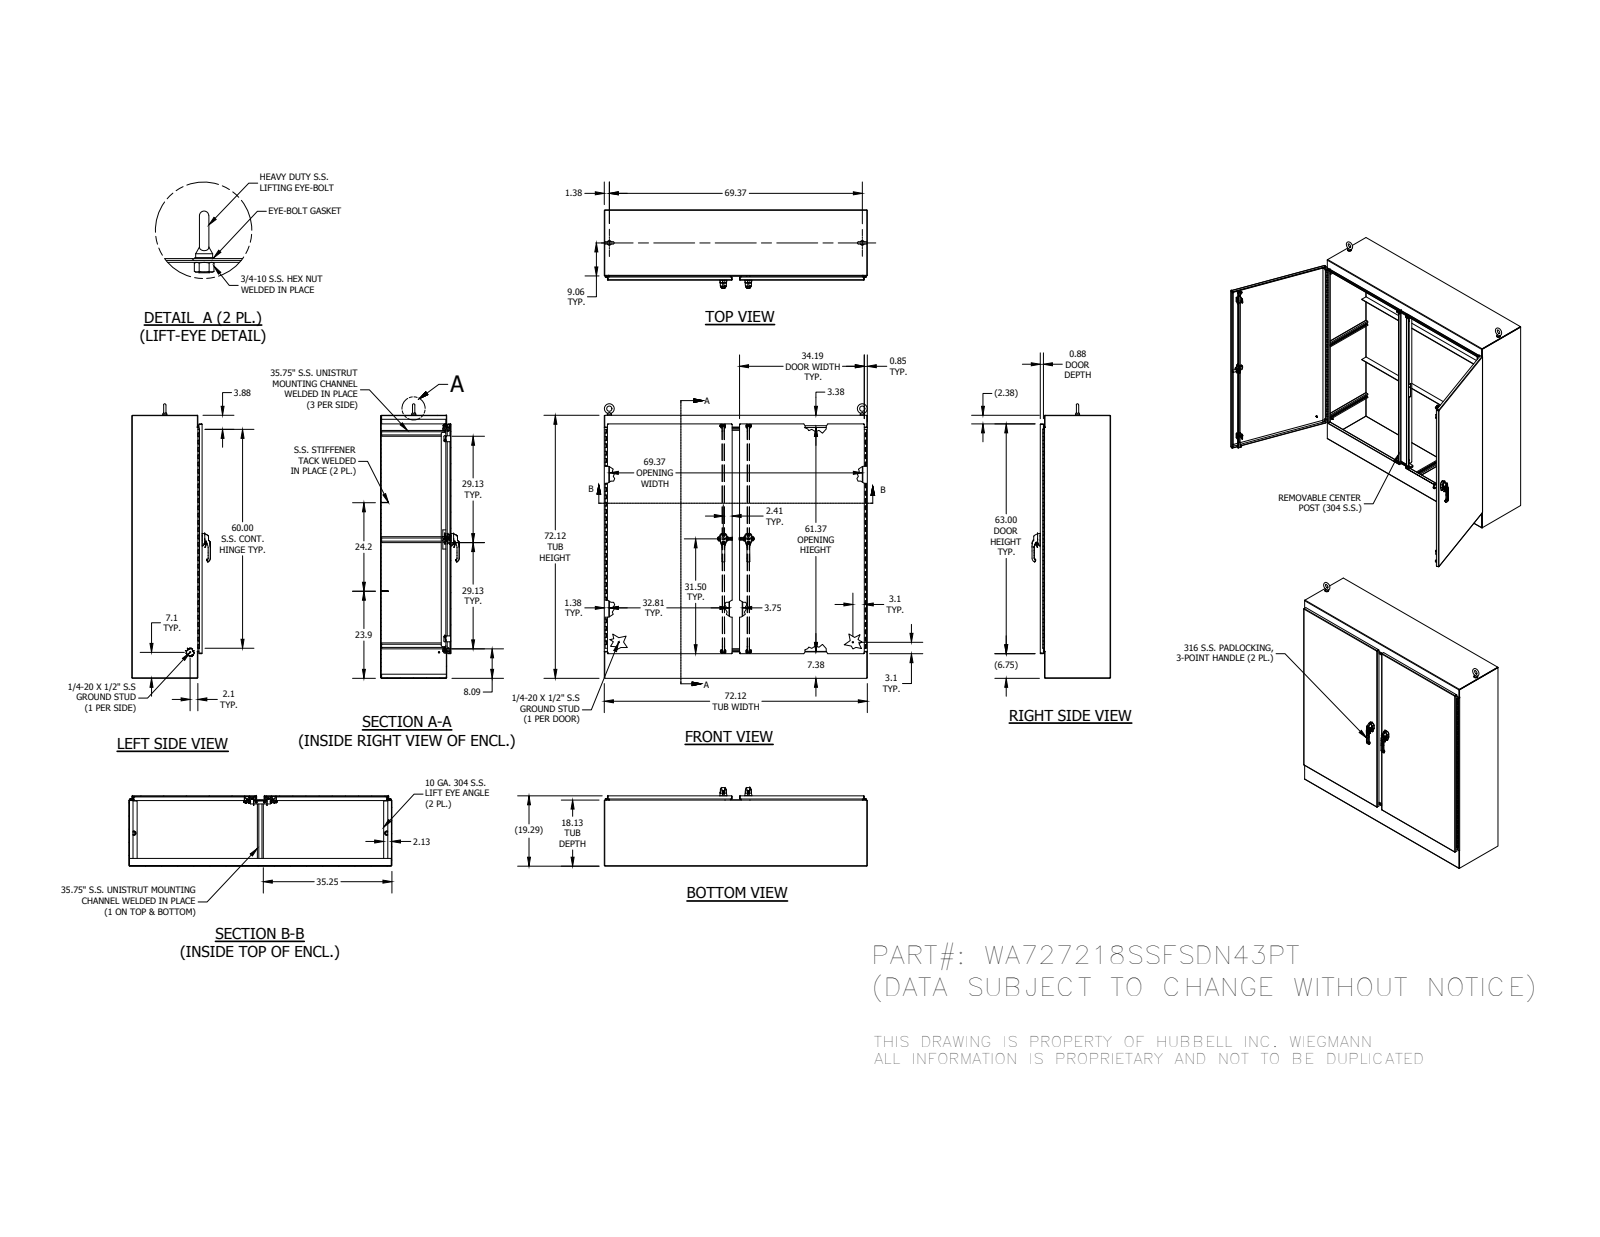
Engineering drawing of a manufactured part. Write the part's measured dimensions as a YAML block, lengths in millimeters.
part_name: "DIN985_M10; D125B_10_5; WA7272SSFSDN43PTLDR; DIN3771_16X2_5 (+8 more)"
step_written_by: "SolidWorks 2014 (AUTOMOTIVE_DESIGN)"
units: millimeters
bodies: {solids: 133, faces: 7024, planar: 2638, cylindrical: 2690, other: 1696}
overall_size: [1911.3, 1832, 547.1]
volume: 38260000
surface_area: 24520000
round_holes:
  - {diameter: 6.7, count: 16}
  - {diameter: 9.5, count: 16}
  - {diameter: 4.7, count: 8}
  - {diameter: 5.4, count: 6}
  - {diameter: 6.4, count: 6}
  - {diameter: 7.1, count: 6}
  - {diameter: 5, count: 4}
  - {diameter: 6.1, count: 4}
  - {diameter: 6.4, count: 4}
  - {diameter: 7.1, count: 4}
  - {diameter: 8, count: 4}
  - {diameter: 10.2, count: 4}
round_bosses_or_shafts:
  - {diameter: 6.4, count: 7}
  - {diameter: 25.4, count: 6}
  - {diameter: 13.5, count: 6}
  - {diameter: 6, count: 6}
  - {diameter: 14.3, count: 4}
  - {diameter: 13.5, count: 4}
  - {diameter: 12.7, count: 4}
  - {diameter: 11.1, count: 4}
partial_cylinders:
  - {radius: 0.5, count: 352}
  - {radius: 0.3, count: 214}
  - {radius: 0.5, count: 44}
  - {radius: 3.2, count: 44}
  - {radius: 1.3, count: 34}
  - {radius: 2, count: 28}
  - {radius: 0.6, count: 24}
  - {radius: 1.5, count: 24}
face_to_face_distances: [3.2, 3.2, 1828.8, 486.8, 1825.6, 1832, 457.2, 29.6, 483.7, 486.8]
hole_center_spacings: [1384, 1403.1, 508, 9.7, 9.7, 169.3, 19.3, 338.7]
